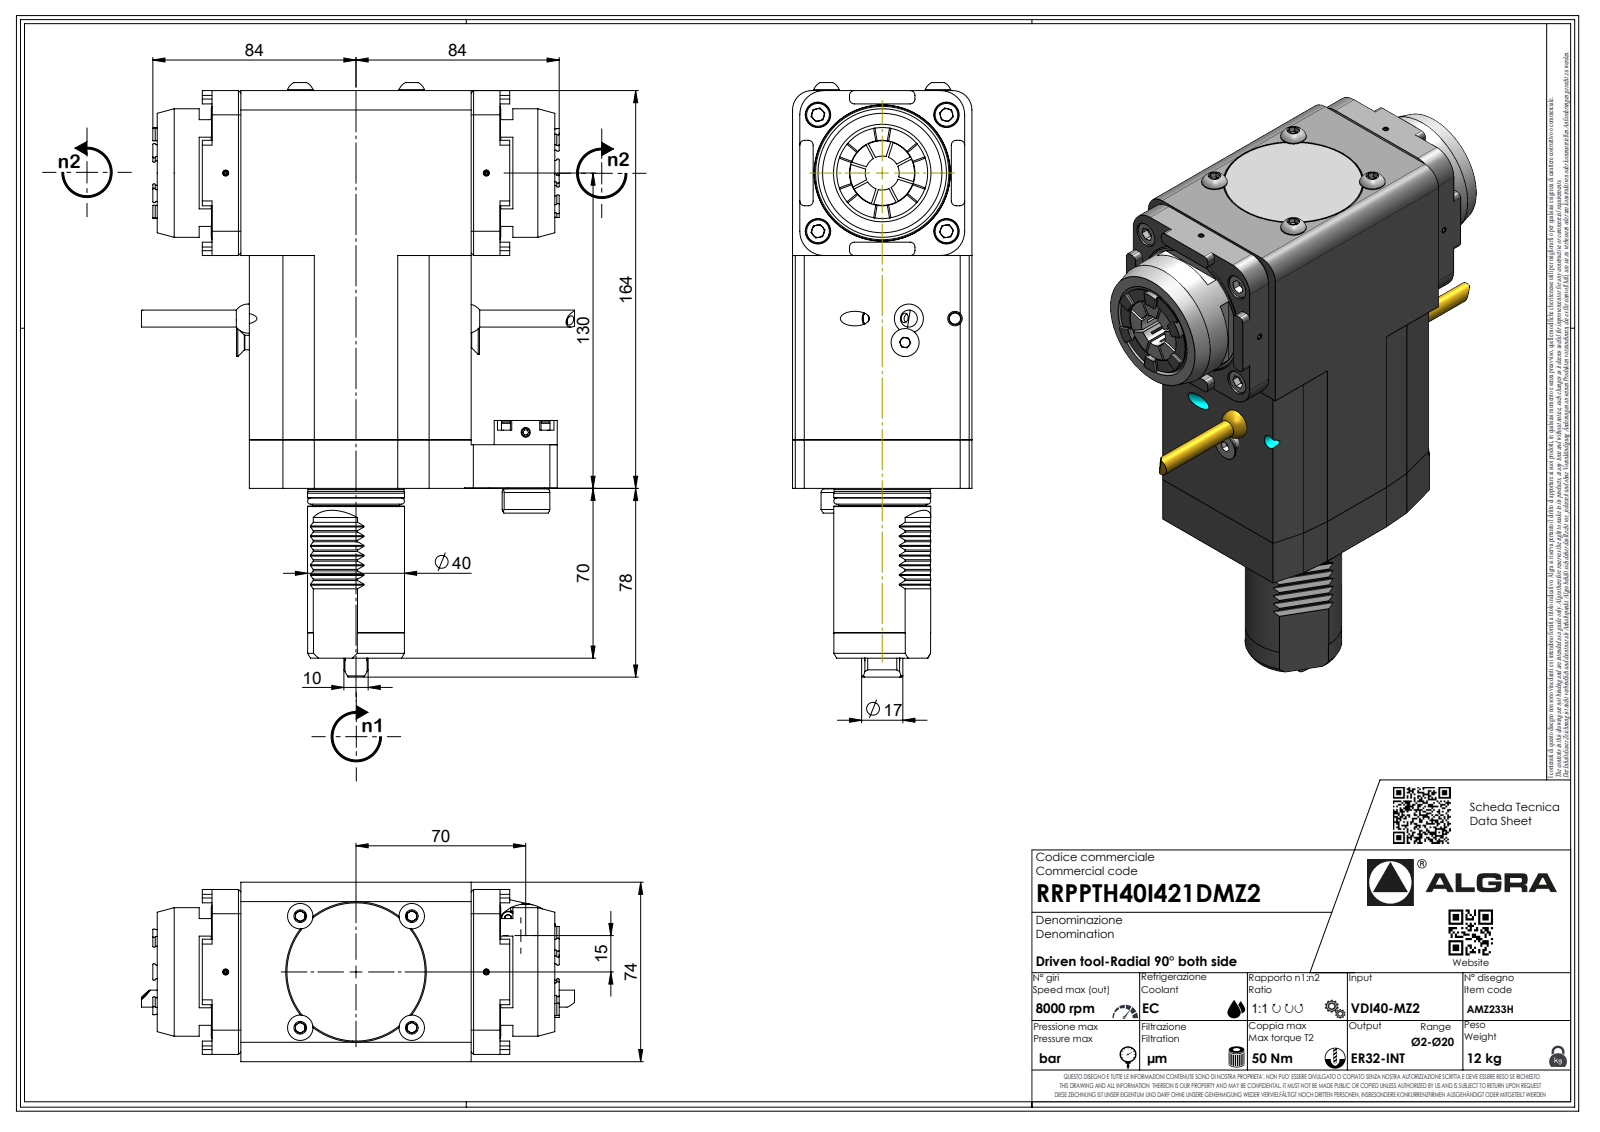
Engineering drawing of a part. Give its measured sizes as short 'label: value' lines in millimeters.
name: RRPPTH40I421DMZ2
written by: SolidWorks 2023 (AUTOMOTIVE_DESIGN)
unit: mm
bodies: 1 solid, 719 faces (434 planar, 141 cylindrical, 144 other)
size: 241.97 × 167.61 × 74
volume: 1 428 000 mm³; area: 104 911 mm²
holes: 1× ⌀2.1
bosses: 4× ⌀5.5, 1× ⌀62.8, 1× ⌀53, 1× ⌀40, 1× ⌀39.9, 1× ⌀39.6, 1× ⌀36, 1× ⌀26
rounds: 38× R2, 8× R1, 8× R10, 7× R0.3, 7× R0.33, 7× R0.52, 7× R3.7, 4× R3
face distances: 74, 164, 91.5, 12, 107, 22.5, 34.5, 129.5, 141.5, 68
